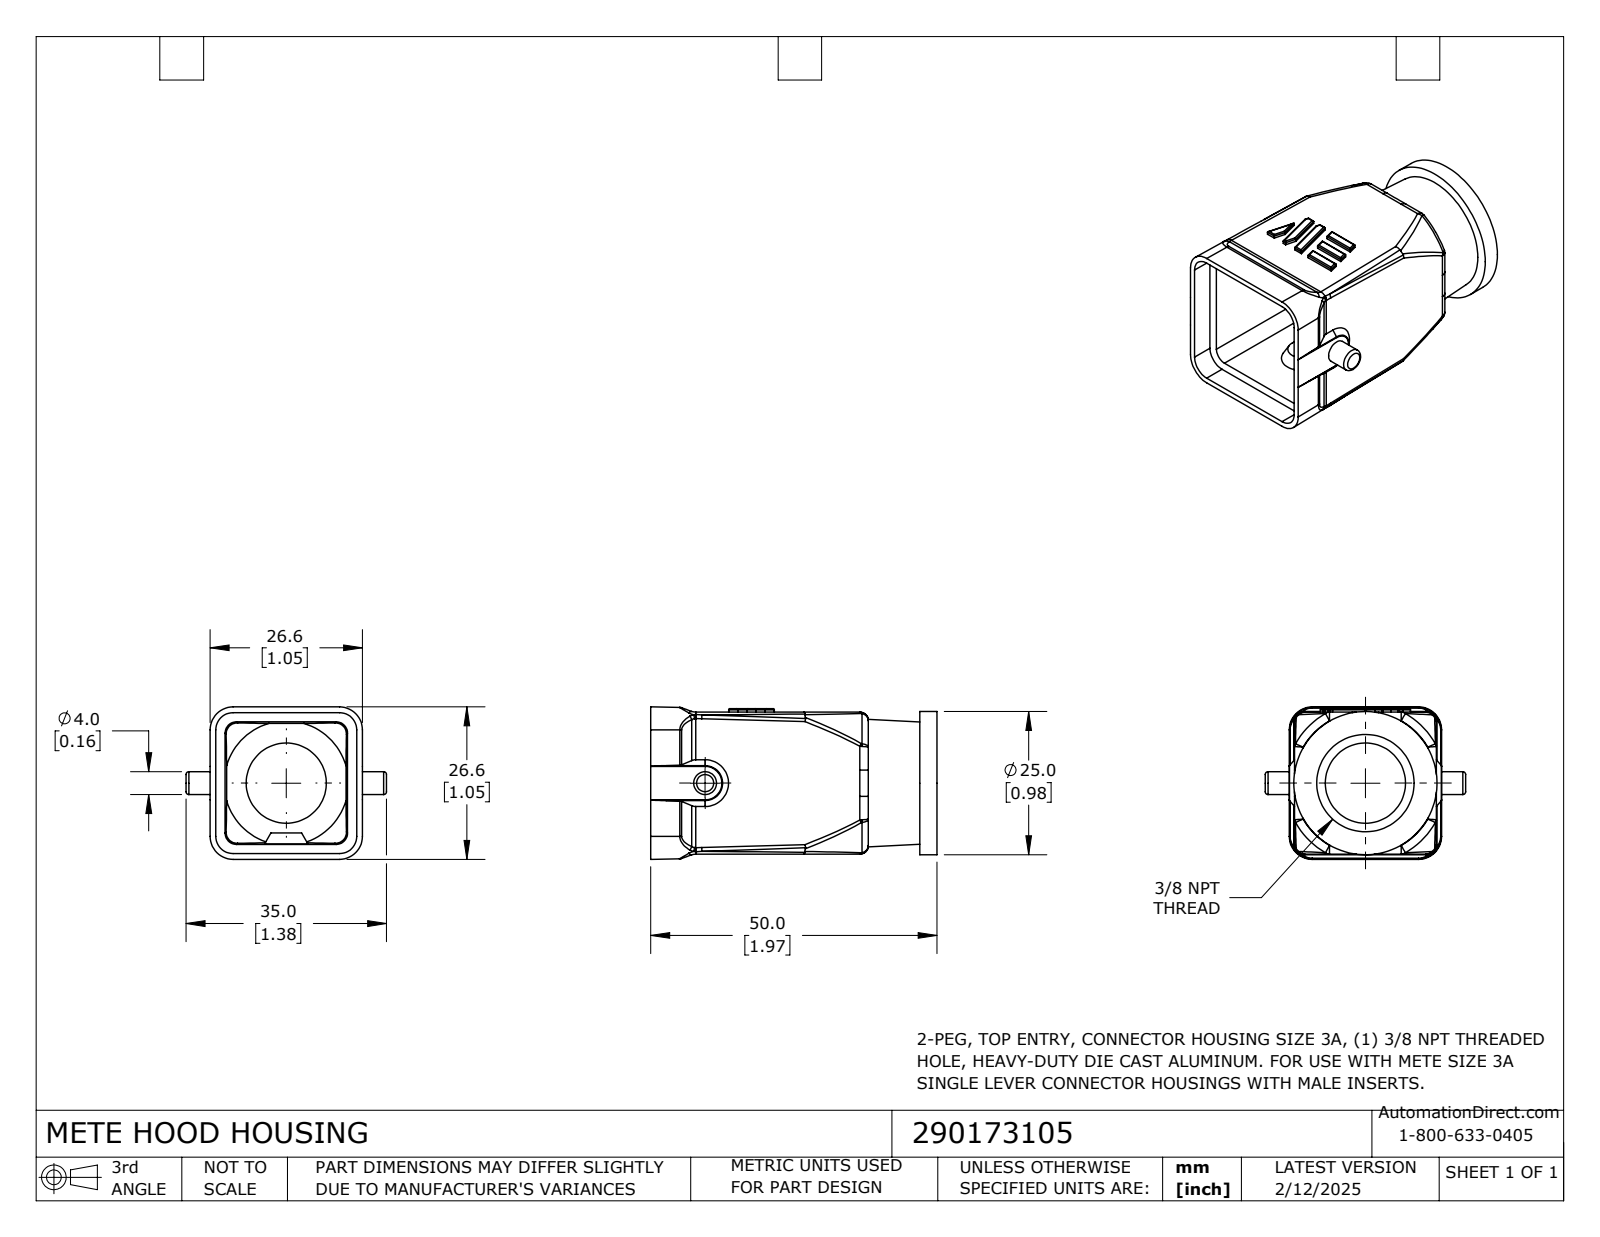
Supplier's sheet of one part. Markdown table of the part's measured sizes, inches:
| quantity | value |
| --- | --- |
| part name | 290173105 |
| STEP written by | SolidWorks 2024 (CONFIG_CONTROL_DESIGN) |
| units | inches |
| bodies | 1 solid, 250 faces (79 planar, 75 cylindrical, 96 other) |
| overall size | 1.969 × 1.378 × 1.047 |
| volume | 0.585 in³ |
| surface area | 14.53 in² |
| round holes (diameter × count) | 0.122 × 1, 0.177 × 1, 0.236 × 1, 0.551 × 1, 0.669 × 1 |
| round bosses / shafts (diameter × count) | 0.984 × 1, 0.157 × 1 |
| partial cylindrical surfaces (radius × count) | 0.008 × 21, 0.079 × 8, 0.059 × 6, 0.118 × 4, 0.039 × 2 |
| main face-to-face distances | 0.976, 0.972, 0.551, 1.268, 1.819, 0.969, 1.701, 0.433, 0.118, 0.145 |
